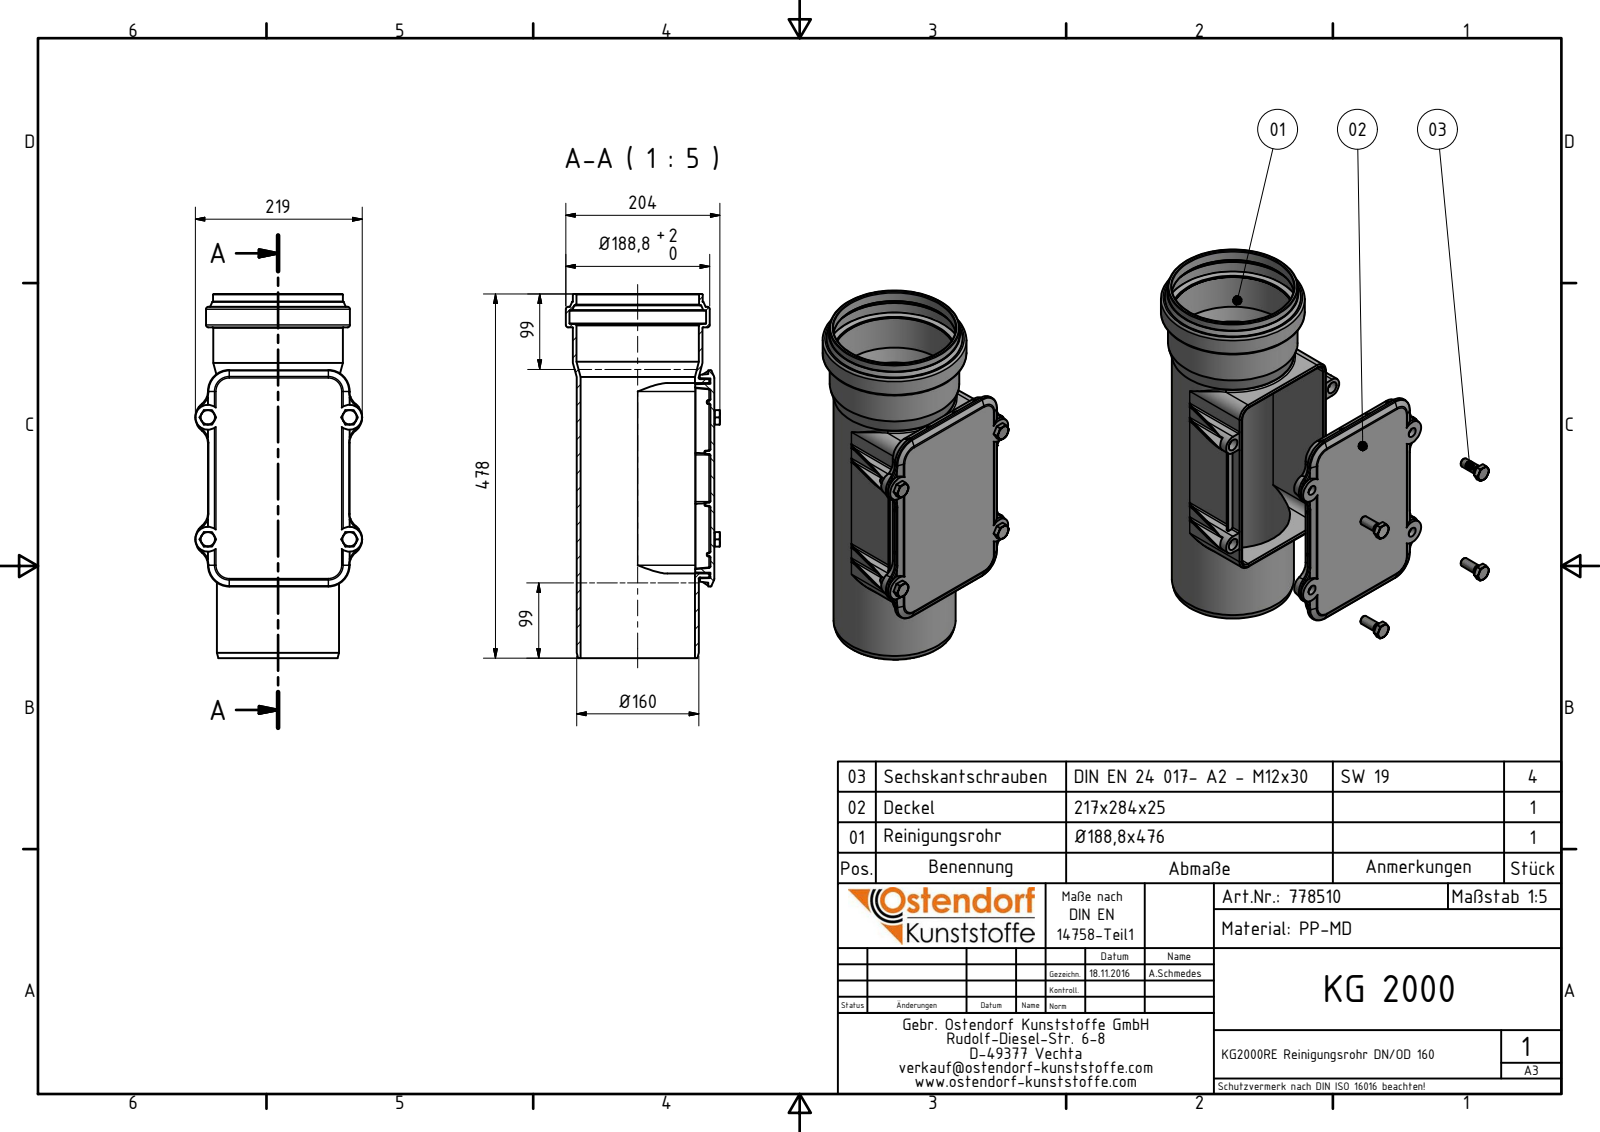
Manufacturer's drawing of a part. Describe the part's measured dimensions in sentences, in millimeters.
The part is named "778510 KG2000RE Reinigungsrohr DN_OD 160; 778510 KG2000RE Reinigungsrohr DN_OD 160 Deckel; DIN 933 - M12 x 30; 778510 KG2000RE Reinigungsrohr DN_OD 160 Zusammenbau". Its 3-D file was written by "Autodesk Inventor 2016 (AUTOMOTIVE_DESIGN)". It is 6 solids with 1262 faces: 331 planar, 423 cylindrical and 508 other. Overall it measures 478 by 219 by 202.4 millimeters. Its volume is 1 769 000 cubic millimeters and its surface area 709 098 square millimeters. Round holes: 4 of diameter 13, 4 of diameter 16, 1 of diameter 150, 1 of diameter 160.7, 1 of diameter 161, 1 of diameter 179.4. Round bosses or shafts: 4 of diameter 17.2, 4 of diameter 12, 4 of diameter 11.05, 1 of diameter 188.8, 1 of diameter 170.4, 1 of diameter 170.1, 1 of diameter 160.2. Partial cylindrical surfaces (rounded edges, fillets, slot ends): 104 of radius 1, 48 of radius 0.5, 42 of radius 2, 14 of radius 5, 8 of radius 20, 4 of radius 1.5, 4 of radius 3.4, 4 of radius 10.95. The main face-to-face distances are 5.1, 155.1, 5, 150, 160.2, 3, 8, 20, 19, 17. The hole center spacings are 160, 2, 160.01, 184, 186, 243.84, 245.35.
